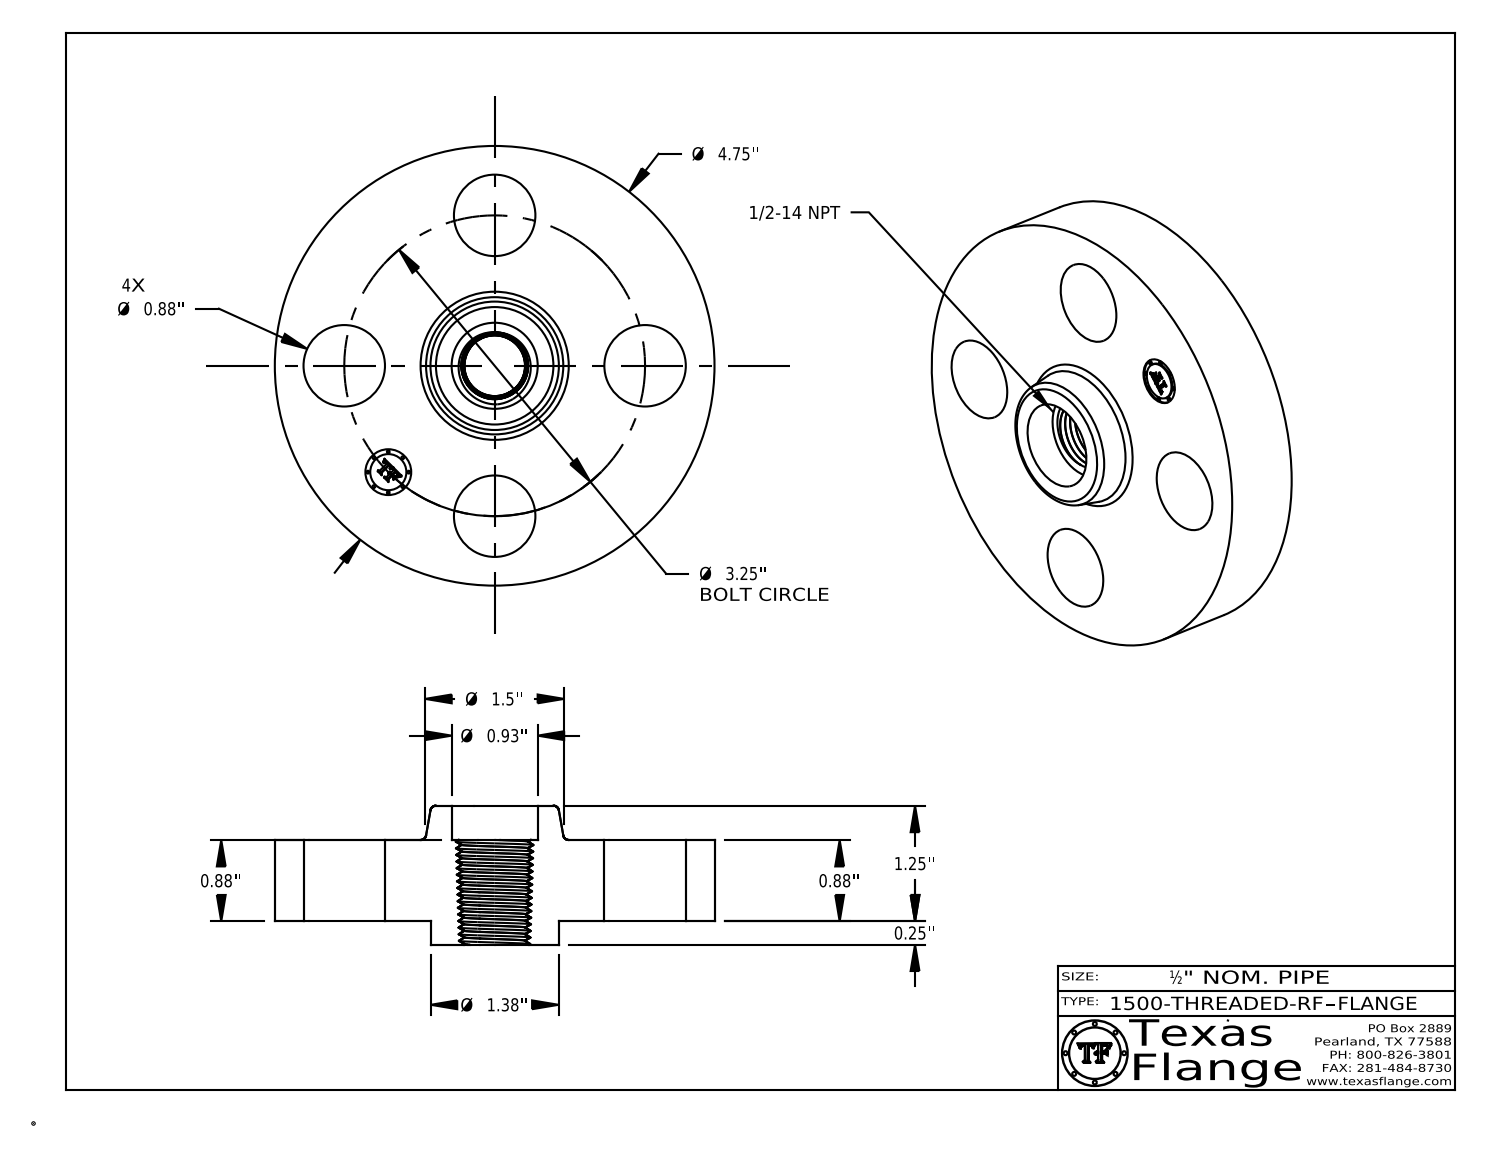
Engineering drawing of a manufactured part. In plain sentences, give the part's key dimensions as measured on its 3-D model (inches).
The part is named "1500-THREADED-RF". Its 3-D file was written by "CATIA V5 STEP AP214 (AUTOMOTIVE_DESIGN)". It is 1 solid with 573 faces: 370 planar, 34 cylindrical and 169 other. Overall it measures 4.75 by 4.75 by 1.5 inches. Its volume is 13.68 cubic inches and its surface area 61 square inches. Round holes: 4 of diameter 0.88, 1 of diameter 0.495, 1 of diameter 0.93. Round bosses or shafts: 8 of diameter 0.03, 1 of diameter 4.75, 1 of diameter 1.38, 1 of diameter 0.39. The main face-to-face distances are 0.88, 0.25, 1.13, 1.5, 1.25, 0.37, 1.115, 0.865, 0.015, 0.385. The hole center spacings are 1.625, 2.298, 1.244, 3.003, 3.25.
